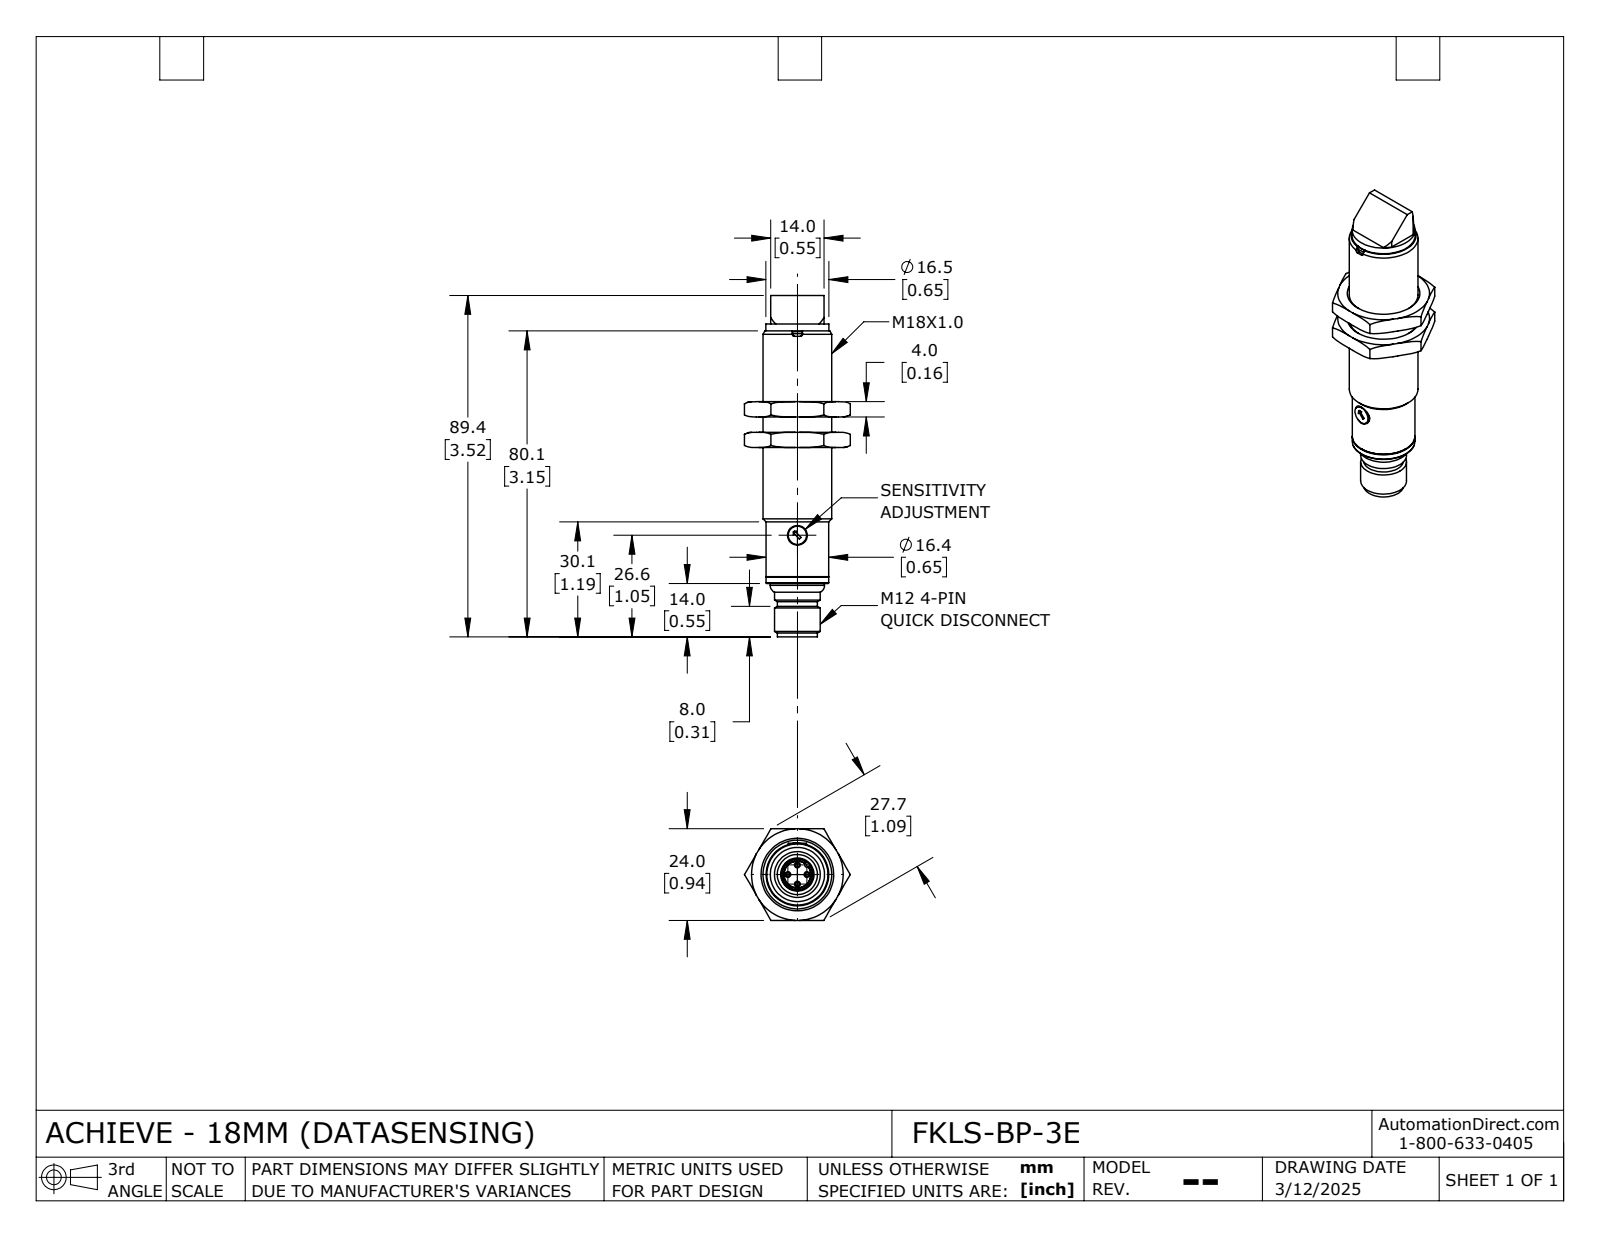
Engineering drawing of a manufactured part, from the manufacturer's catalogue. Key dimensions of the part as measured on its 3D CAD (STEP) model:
Part name (STEP PRODUCT): FKLS-BP-3E_Default
STEP written by: SolidWorks 2024 (CONFIG_CONTROL_DESIGN)
Units: inches
Bodies: 4 solids, 155 faces (67 planar, 35 cylindrical, 53 other)
Overall size (bounding box): 3.52 × 1.091 × 0.945
Volume: 1.231 in³ · Surface area: 13.64 in²
Round holes (diameter × count): ⌀0.106 ×1, ⌀0.185 ×1, ⌀0.278 ×1, ⌀0.327 ×1, ⌀0.591 ×1, ⌀0.622 ×1, ⌀0.709 ×1
Round bosses / shafts (diameter × count): ⌀0.039 ×4, ⌀0.65 ×1, ⌀0.646 ×1, ⌀0.559 ×1, ⌀0.472 ×1, ⌀0.413 ×1, ⌀0.276 ×1, ⌀0.189 ×1
Partial cylindrical surfaces — rounded edges, fillets, slot ends (radius × count): R0.02 ×4, R0.024 ×1, R0.317 ×1, R0.331 ×1
Main face-to-face distances: 0.157, 0.315, 0.945, 0.472, 0.115, 0.016, 0.131, 0.11, 0.094, 0.02
